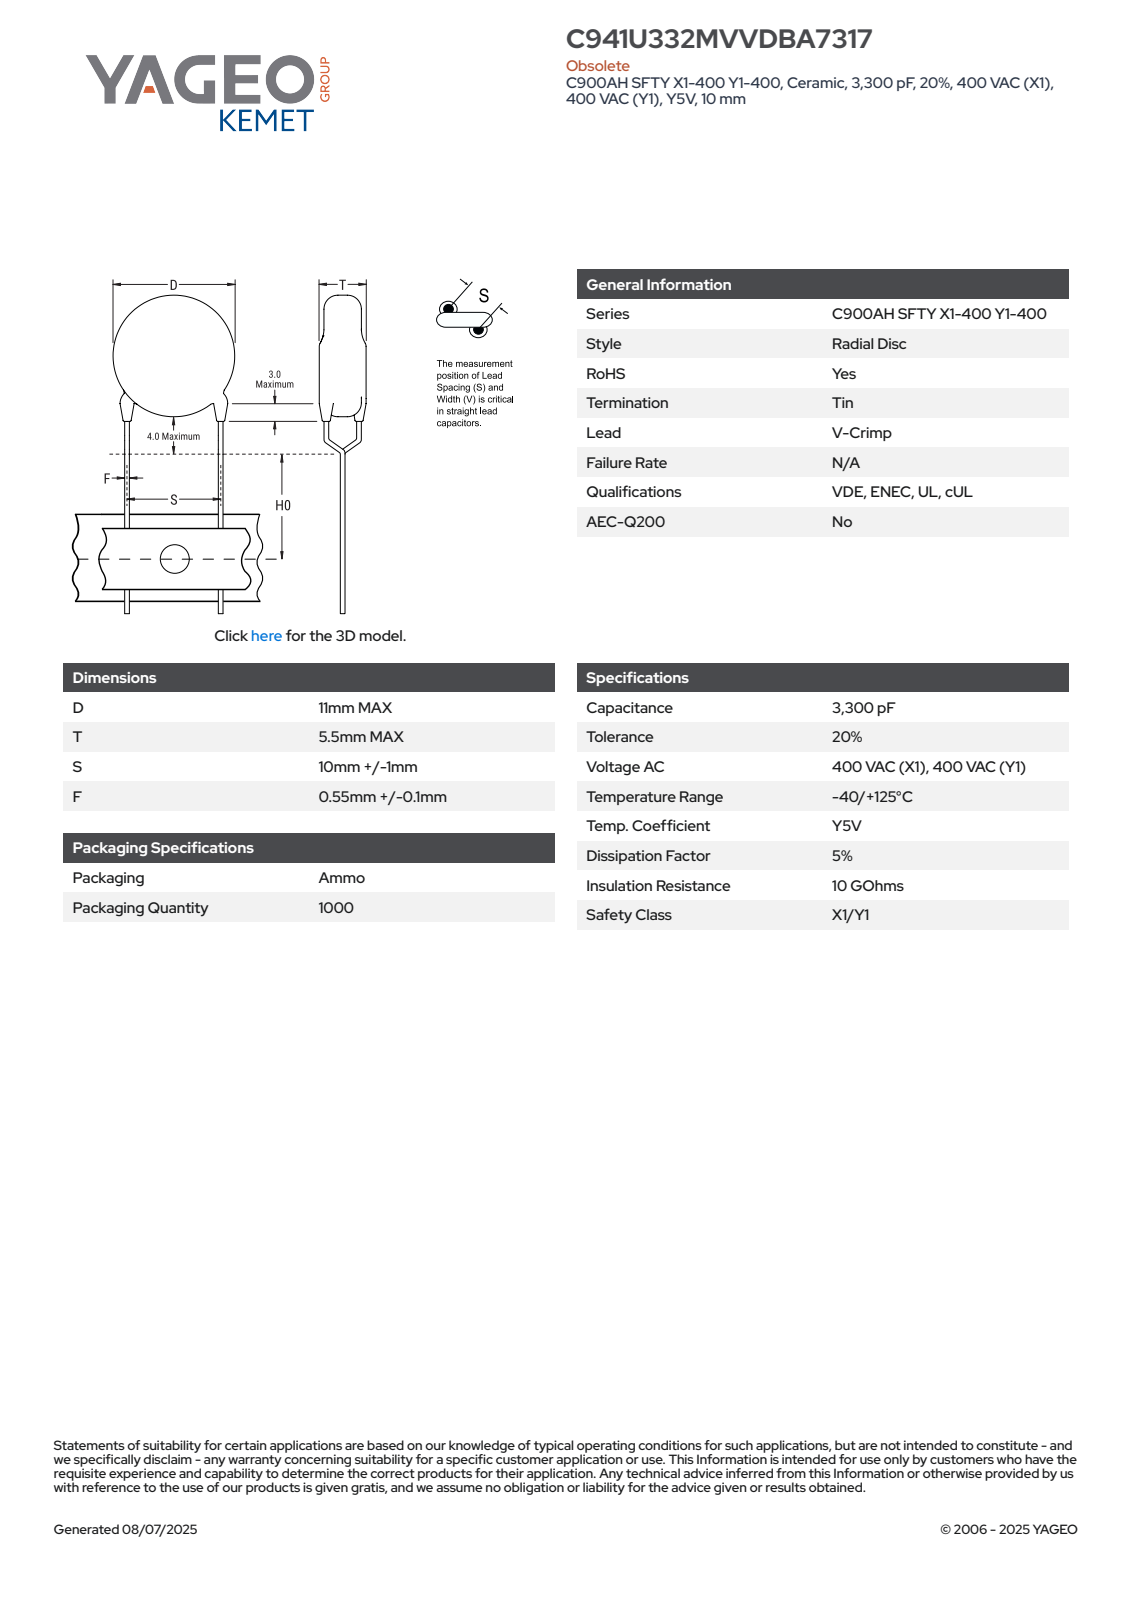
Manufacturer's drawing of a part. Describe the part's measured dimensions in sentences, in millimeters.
The part is named "CCD_VCC900_D11T5.5S10LL20F0.65". Its 3-D file was written by "SolidWorks 2014 (AUTOMOTIVE_DESIGN)". It is 5 solids with 93 faces: 65 planar, 16 cylindrical and 12 other. Overall it measures 34.8 by 11 by 5.5 millimeters. Its volume is 528 cubic millimeters and its surface area 473 square millimeters. Round bosses or shafts: 6 of diameter 0.65, 1 of diameter 11. The main face-to-face distances are 5.5, 22.9, 30.01, 7.11, 28.58, 5.68, 1.43, 0.39, 0.35, 5.84.
